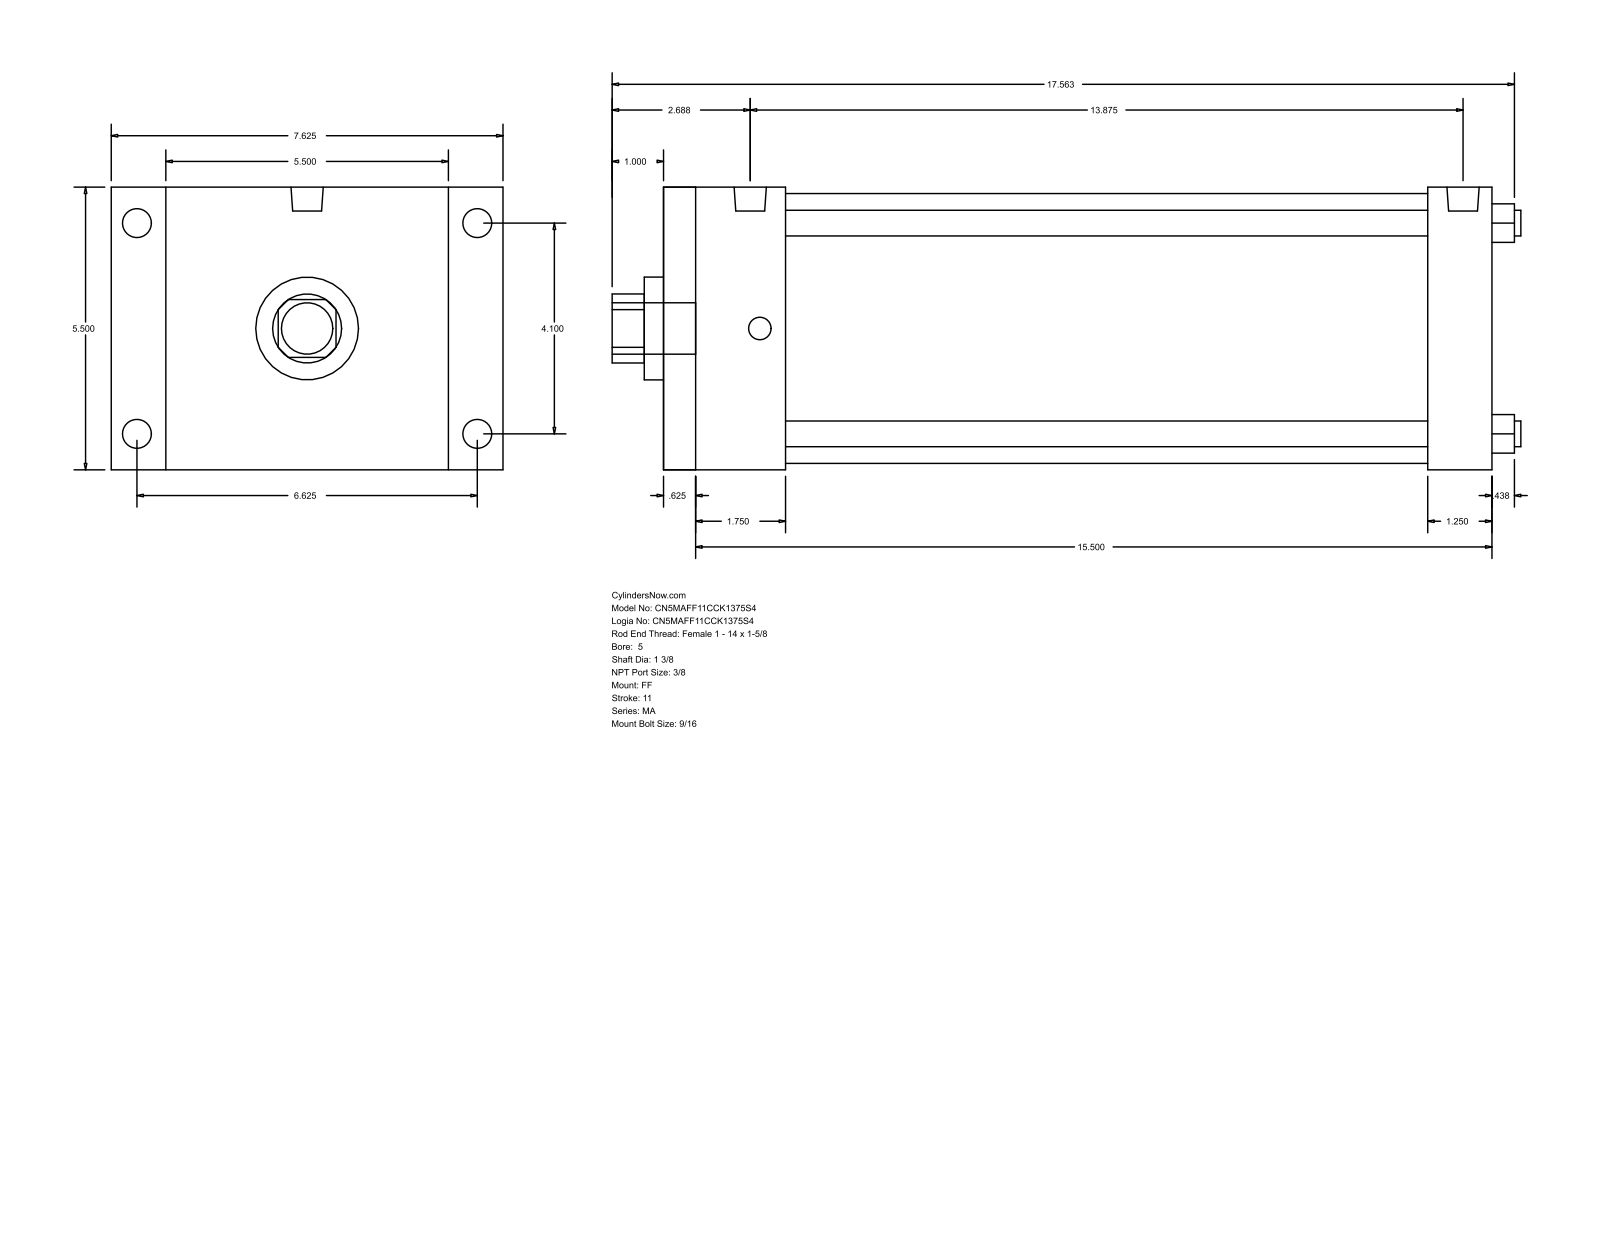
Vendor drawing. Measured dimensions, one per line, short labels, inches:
name: MA_FF__0500_1.375
written by: GSSL Pune (CONFIG_CONTROL_DESIGN)
unit: in
bodies: 0 solids, 92 faces (64 planar, 28 cylindrical, 0 other)
size: 17.687 × 7.625 × 5.5
holes: 4× ⌀0.5, 1× ⌀1.375, 1× ⌀2, 1× ⌀5.25
bosses: 4× ⌀0.563, 4× ⌀0.437, 2× ⌀0.627, 1× ⌀1
rounds: 1× R0.672
face distances: 5.5, 16.125, 0.625, 15.5, 14.875, 14.25, 1.25, 2.375, 1.75, 12.5
hole spacings: 2.899, 4.1, 5.798
